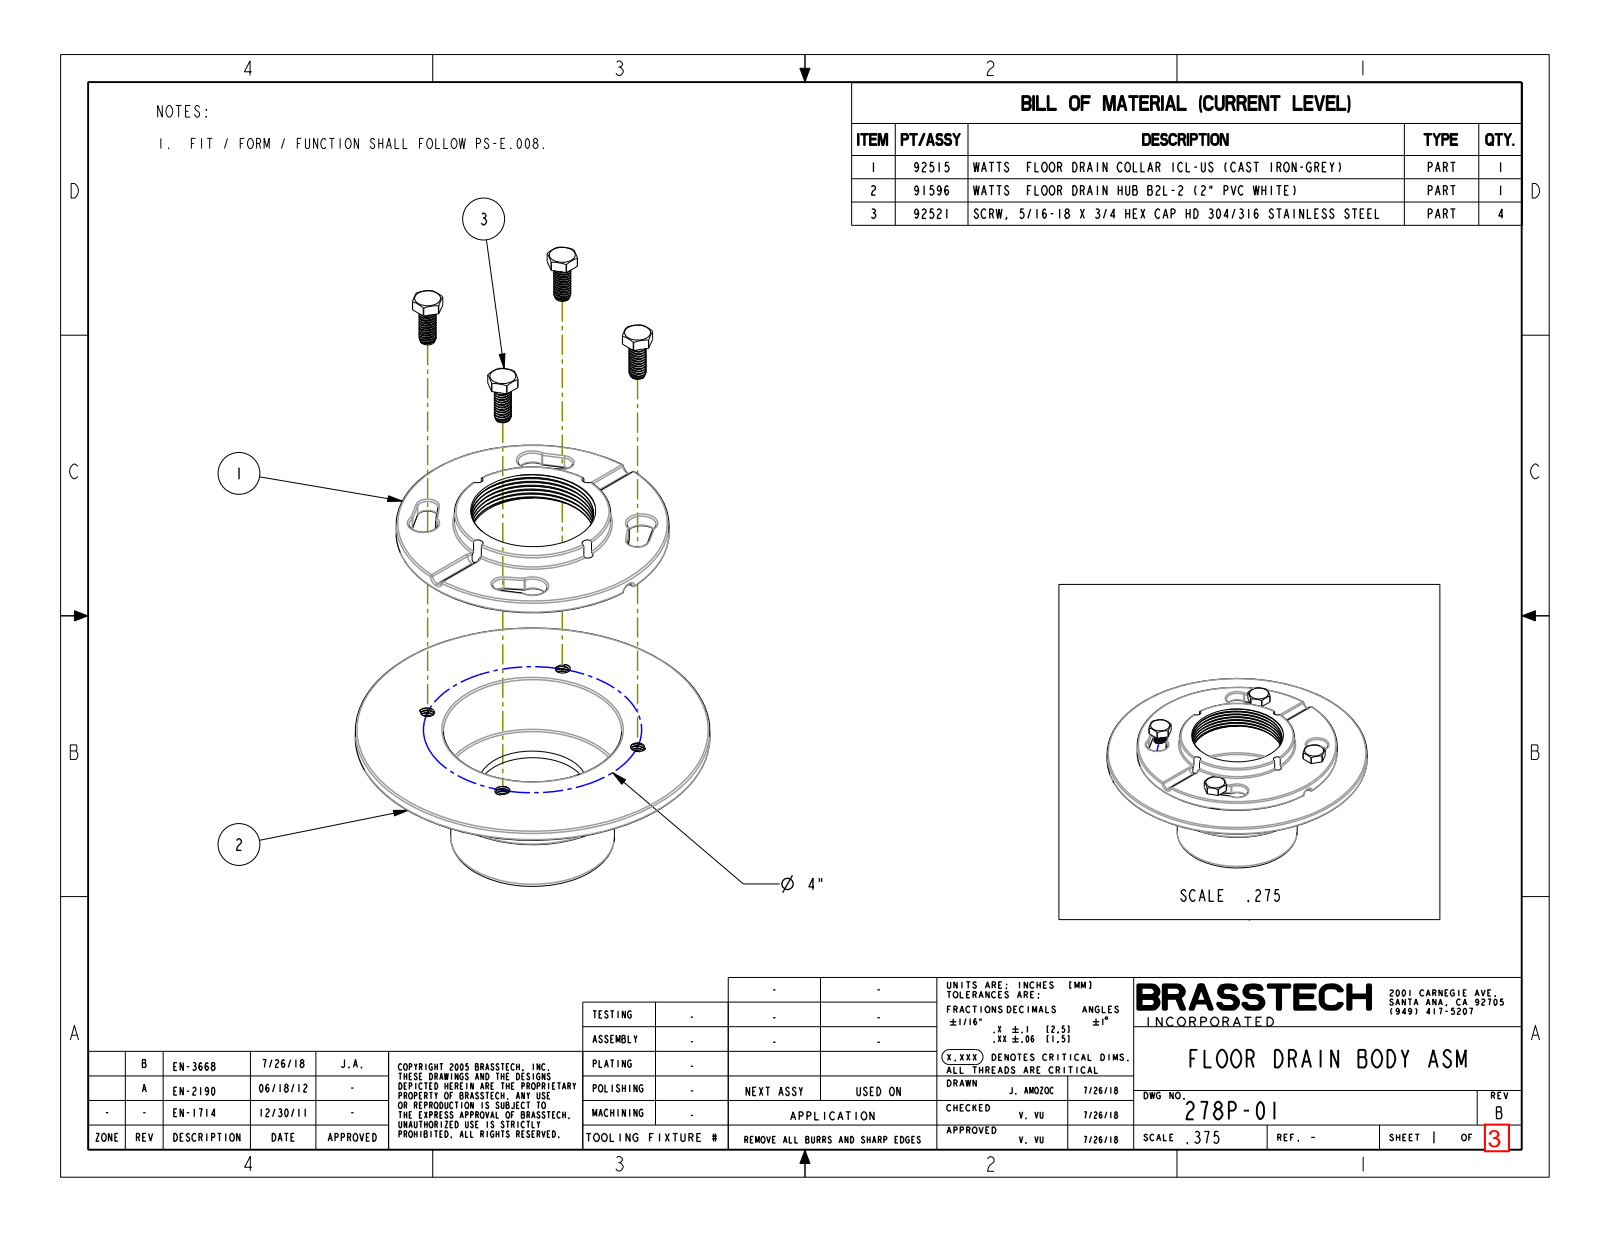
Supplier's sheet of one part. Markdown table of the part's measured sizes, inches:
| quantity | value |
| --- | --- |
| part name | 92515; 91596; 92521; 278P-01_ASM |
| STEP written by | PRO/ENGINEER BY PARAMETRIC TECHNOLOGY CORPORATION, 2013150 (CONFIG_CONTROL_DESIGN) |
| units | inches |
| bodies | 6 solids, 956 faces (86 planar, 438 cylindrical, 432 other) |
| overall size | 6.5 × 6.5 × 3.025 |
| volume | 16.13 in³ |
| surface area | 161.9 in² |
| round holes (diameter × count) | 0.18 × 4, 0.257 × 4, 1.97 × 1, 2.24 × 1, 2.4 × 1, 3.265 × 1 |
| round bosses / shafts (diameter × count) | 0.268 × 52, 0.313 × 4, 6.5 × 1, 5 × 1, 3.665 × 1, 3 × 1, 2.864 × 1 |
| partial cylindrical surfaces (radius × count) | 0.03 × 28, 0.04 × 24, 0.375 × 8, 0.12 × 4, 0.134 × 4, 0.187 × 4, 0.265 × 4, 0.286 × 4 |
| main face-to-face distances | 0.2, 0.46, 0.26, 0.975, 1.175, 1.435, 0.125, 1.1, 1.3, 1.56 |
| hole center spacings | 1.55, 2.192, 1.838, 2, 2.828, 3.437, 0.995, 3.07 |
